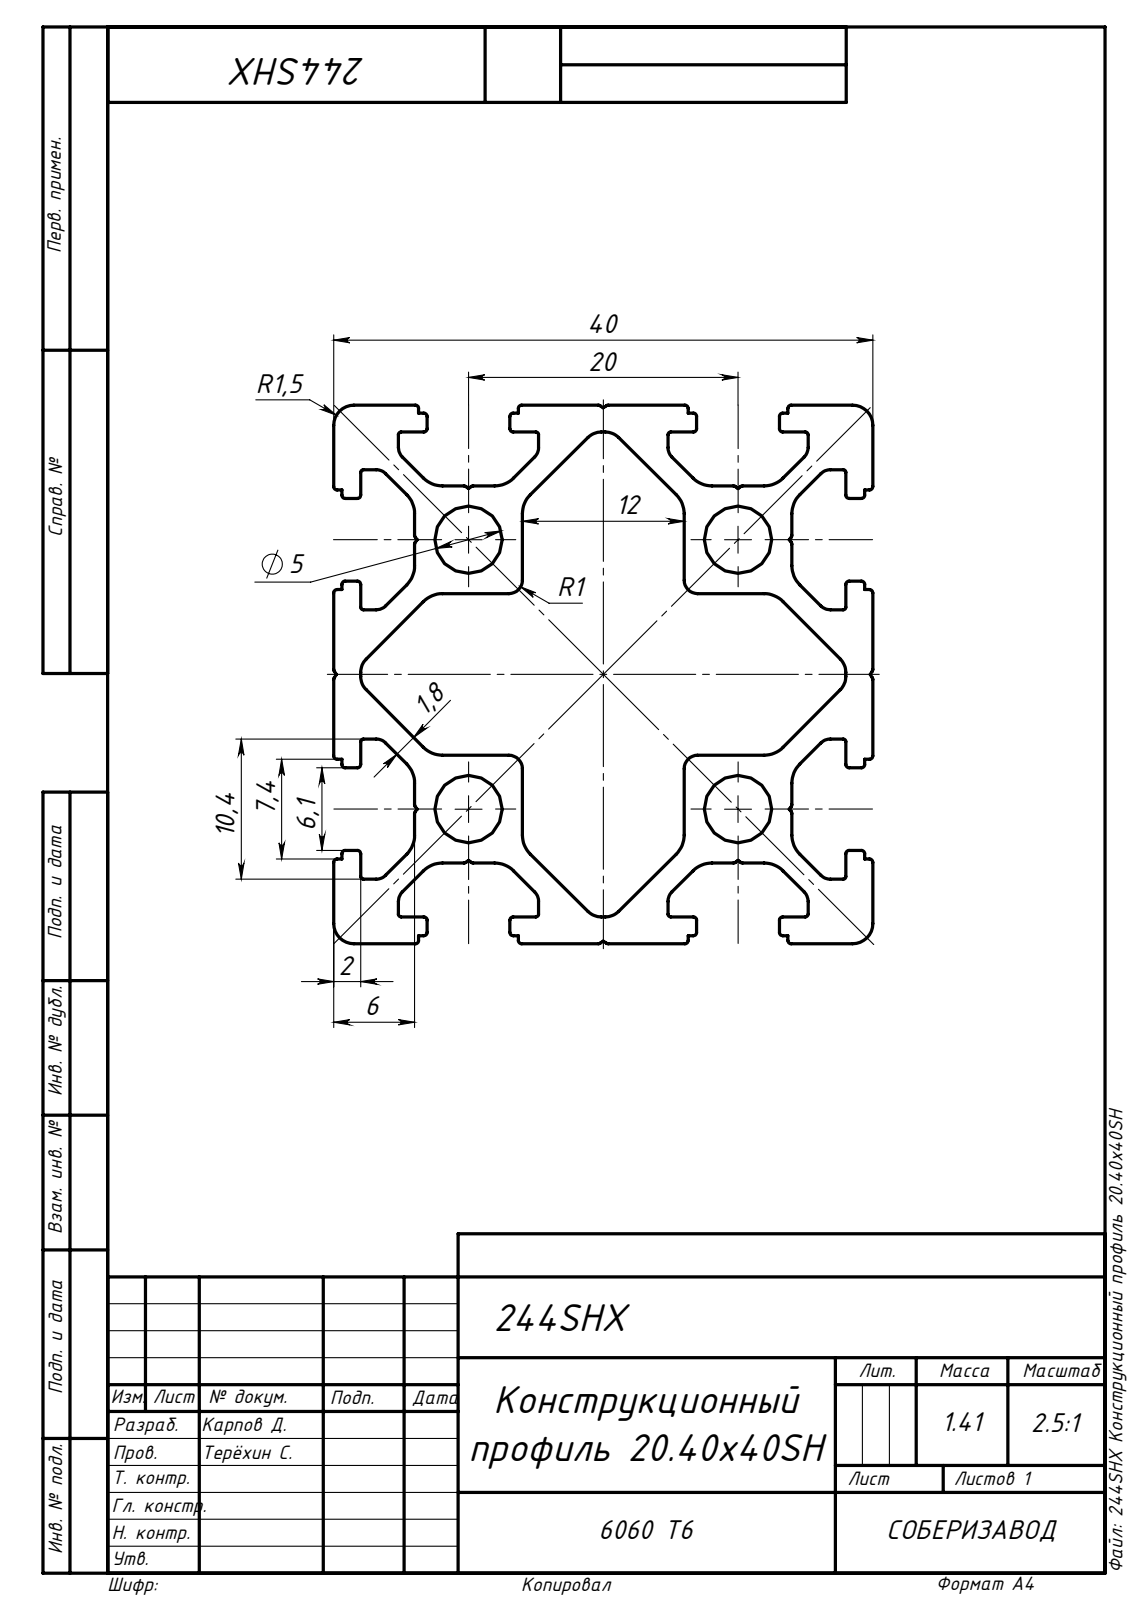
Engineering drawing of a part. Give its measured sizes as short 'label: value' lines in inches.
written by: SolidWorks 2019 (AUTOMOTIVE_DESIGN)
unit: in
bodies: 1 solid, 326 faces (174 planar, 152 cylindrical, 0 other)
size: 39.37 × 1.575 × 1.575
volume: 31.8 in³; area: 731.6 in²
holes: 4× ⌀0.197
rounds: 72× R0.01, 24× R0.079, 20× R0.039, 16× R0.008, 8× R0.055, 4× R0.059
face distances: 0.472, 1.575, 0.787, 0.551, 1.024, 0.079, 1.496, 0.945, 0.236, 1.339
hole spacings: 0.787, 1.113
